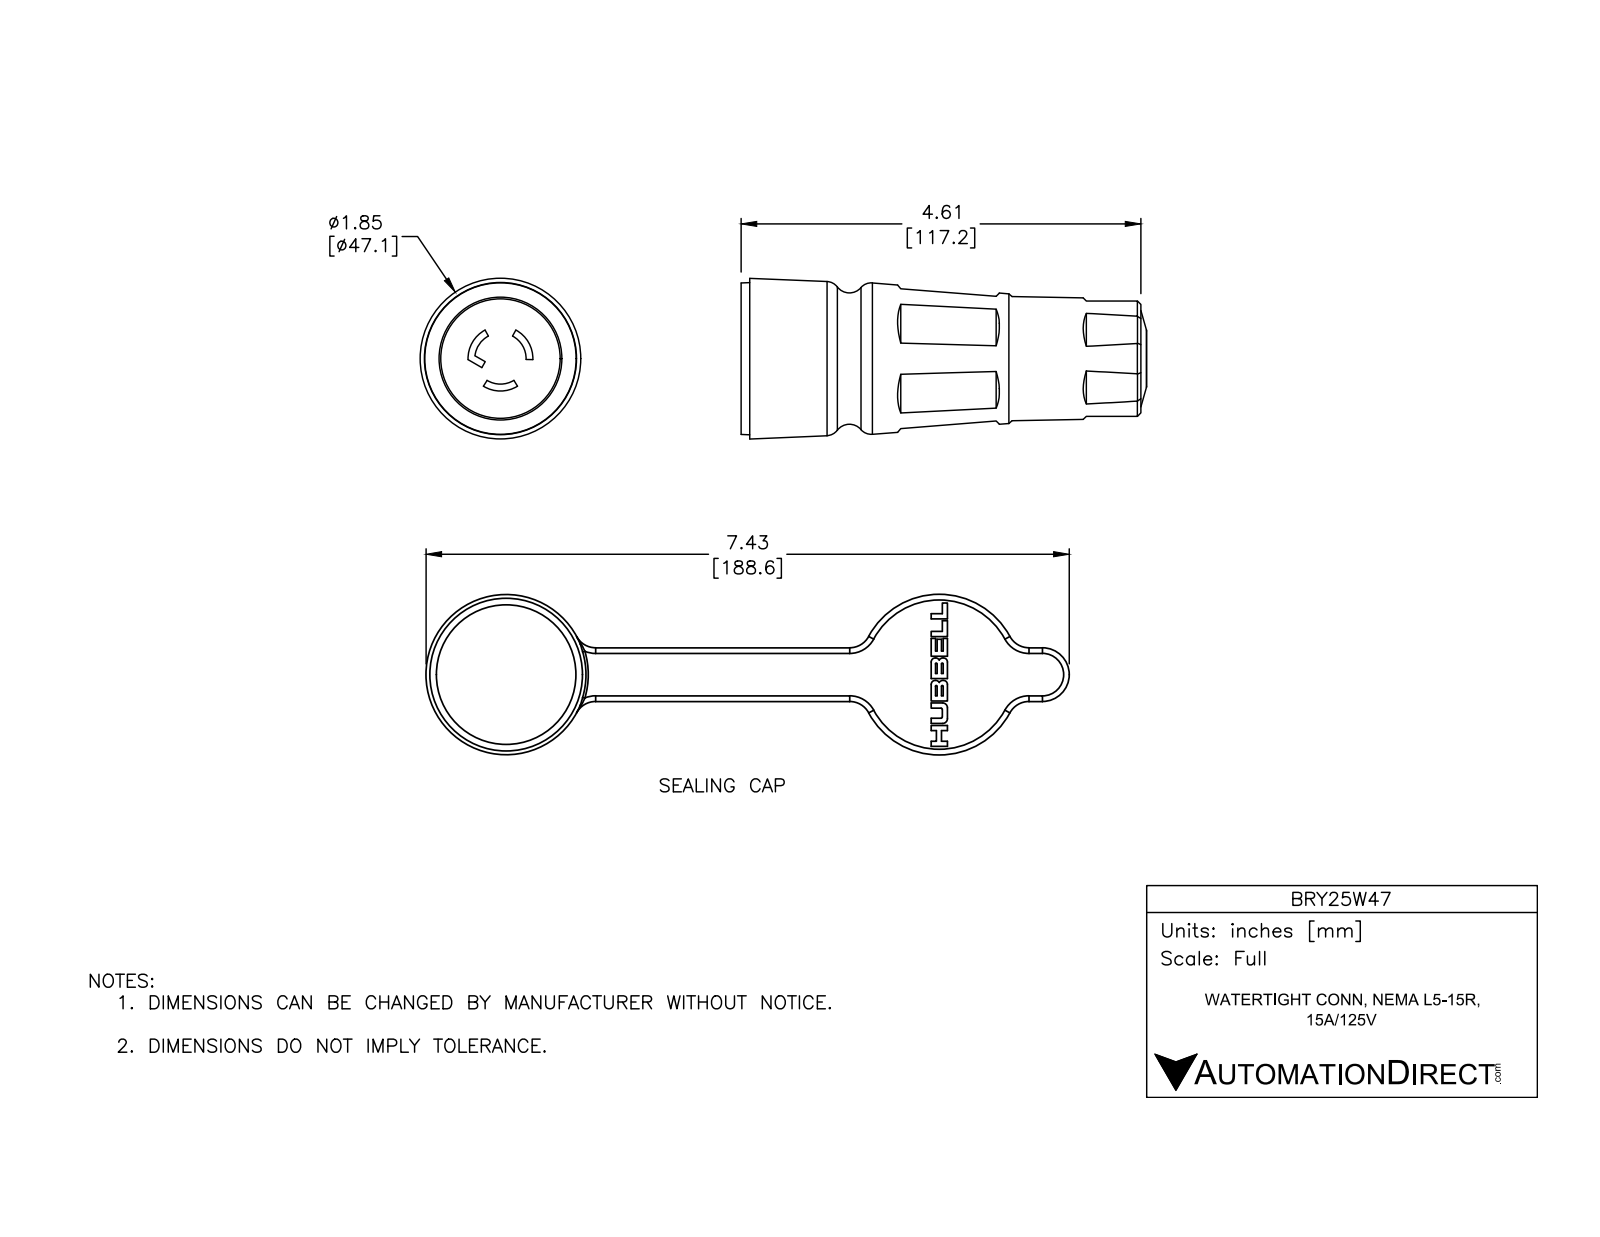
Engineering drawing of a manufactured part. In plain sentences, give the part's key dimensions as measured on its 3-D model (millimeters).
The part is named "BRY25W47-CONNECTOR; BRY25W-CAP; BRY25W47". Its 3-D file was written by "SolidWorks 2016 (AUTOMOTIVE_DESIGN)". It is 5 solids with 183 faces: 76 planar, 51 cylindrical and 56 other. Overall it measures 187 by 118.9 by 47.1 millimeters. Its volume is 142 500 cubic millimeters and its surface area 50 630 square millimeters. Round holes: 1 of diameter 14.2, 1 of diameter 28.2, 1 of diameter 31, 1 of diameter 36, 1 of diameter 39. Round bosses or shafts: 1 of diameter 47, 1 of diameter 45, 1 of diameter 42.3, 1 of diameter 37.4, 1 of diameter 35, 1 of diameter 25.2. Partial cylindrical surfaces (rounded edges, fillets, slot ends): 4 of radius 1.5, 4 of radius 6, 2 of radius 4, 1 of radius 7.5, 1 of radius 8, 1 of radius 9.5. The main face-to-face distances are 3.3, 8.6, 11.9, 27, 18.4, 15.1, 42, 14.2, 5.6, 2.4. The hole center spacings are 125.5.
